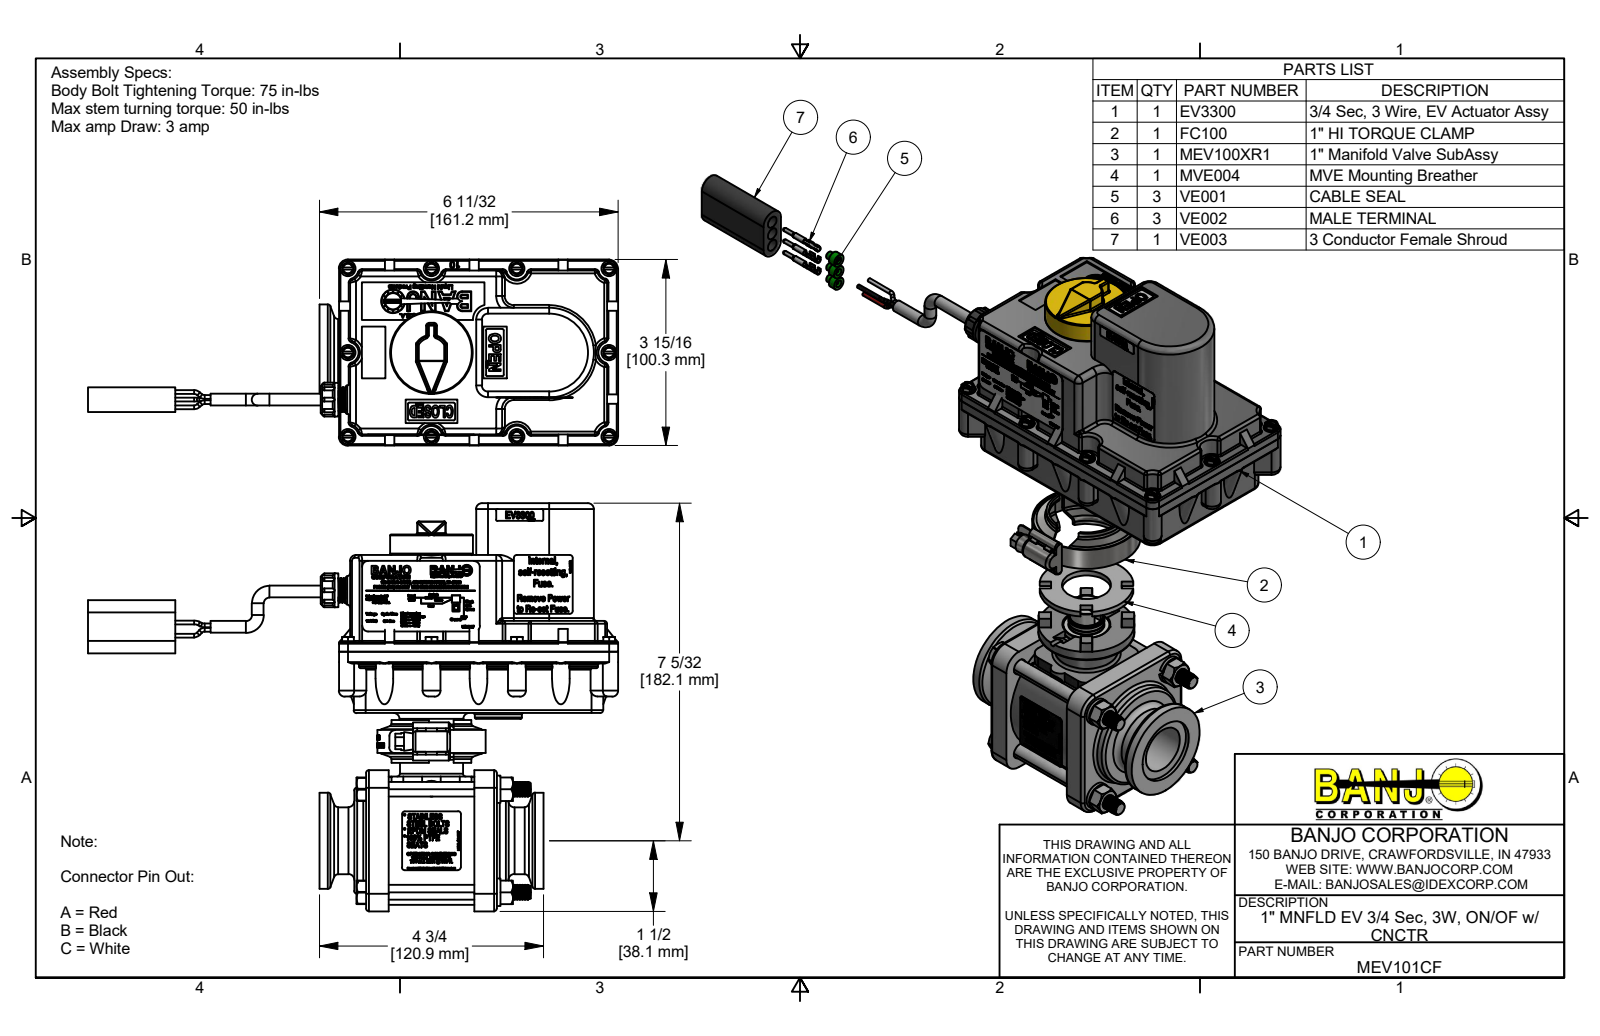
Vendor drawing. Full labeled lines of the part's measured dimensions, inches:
Part name (STEP PRODUCT): MEV101CF; MEV100XR1; MEV10254A; MEV10254AX (+8 more)
STEP written by: Autodesk Inventor 2019 (AUTOMOTIVE_DESIGN)
Units: inches
Bodies: 79 solids, 14191 faces (7114 planar, 1769 cylindrical, 5308 other)
Overall size (bounding box): 11.261 × 8.668 × 3.95
Volume: 56.37 in³ · Surface area: 629.1 in²
Round holes (diameter × count): ⌀0.11 ×10, ⌀0.16 ×10, ⌀0.2 ×10, ⌀0.15 ×9, ⌀0.052 ×8, ⌀0.079 ×8, ⌀0.047 ×6, ⌀0.12 ×6, ⌀0.176 ×6, ⌀0.015 ×4, ⌀0.25 ×4, ⌀0.252 ×4
Round bosses / shafts (diameter × count): ⌀0.268 ×60, ⌀0.08 ×12, ⌀0.328 ×10, ⌀0.138 ×10, ⌀0.103 ×8, ⌀0.25 ×6, ⌀0.075 ×5, ⌀0.583 ×4
Partial cylindrical surfaces — rounded edges, fillets, slot ends (radius × count): R0.03 ×132, R0.06 ×67, R0.02 ×62, R0.035 ×43, R0.125 ×32, R0.315 ×24, R0.5 ×24, R0.062 ×21
Main face-to-face distances: 0.125, 0.125, 2.3, 1.1, 0.2, 0.79, 0.78, 2.565, 1.3, 3.23
Hole centre spacings: 1.68, 2.058, 1.684, 1.785, 2.376, 0.109, 0.492, 1.188
